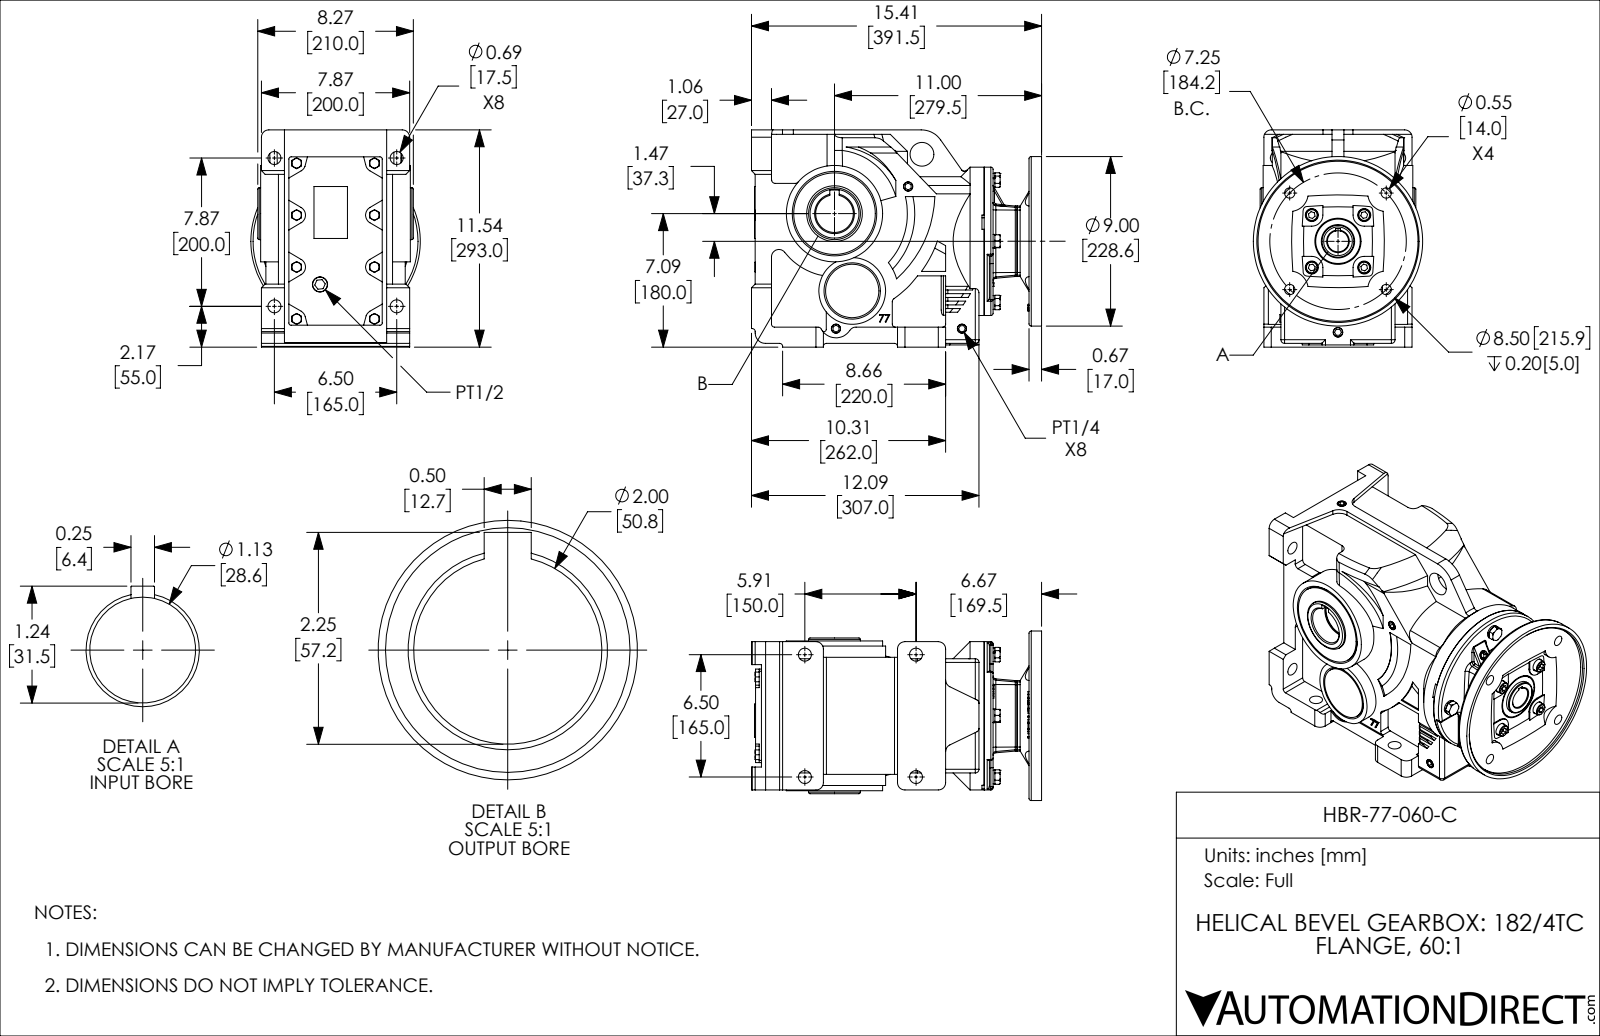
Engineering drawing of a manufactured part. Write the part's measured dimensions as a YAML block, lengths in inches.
part_name: "HBR-77-060-C"
step_written_by: "SolidWorks 2018 (AUTOMOTIVE_DESIGN)"
units: inches
bodies: {solids: 43, faces: 1761, planar: 783, cylindrical: 582, other: 396}
overall_size: [15.413, 11.535, 9]
volume: 339.1
surface_area: 1869
round_holes:
  - {diameter: 0.689, count: 12}
  - {diameter: 0.268, count: 8}
  - {diameter: 0.335, count: 8}
  - {diameter: 0.354, count: 8}
  - {diameter: 0.433, count: 8}
  - {diameter: 0.394, count: 4}
  - {diameter: 0.402, count: 4}
  - {diameter: 0.551, count: 4}
  - {diameter: 0.438, count: 3}
  - {diameter: 0.118, count: 2}
  - {diameter: 0.487, count: 2}
  - {diameter: 2.165, count: 2}
round_bosses_or_shafts:
  - {diameter: 0.315, count: 8}
  - {diameter: 0.63, count: 5}
  - {diameter: 0.724, count: 4}
  - {diameter: 0.394, count: 4}
  - {diameter: 9, count: 1}
  - {diameter: 7.874, count: 1}
  - {diameter: 5.118, count: 1}
  - {diameter: 3.543, count: 1}
partial_cylinders:
  - {radius: 0.394, count: 36}
  - {radius: 0.118, count: 14}
  - {radius: 0.197, count: 12}
  - {radius: 0.315, count: 12}
  - {radius: 0.157, count: 11}
  - {radius: 0.472, count: 10}
  - {radius: 0.591, count: 7}
  - {radius: 0.079, count: 5}
face_to_face_distances: [0.236, 0.472, 0.315, 4.961, 0.276, 5.748, 0.787, 5.276, 0.512, 0.551]
hole_center_spacings: [2.653, 2.756, 4.844, 4.968, 6.352, 6.496, 1.656, 2.32]
